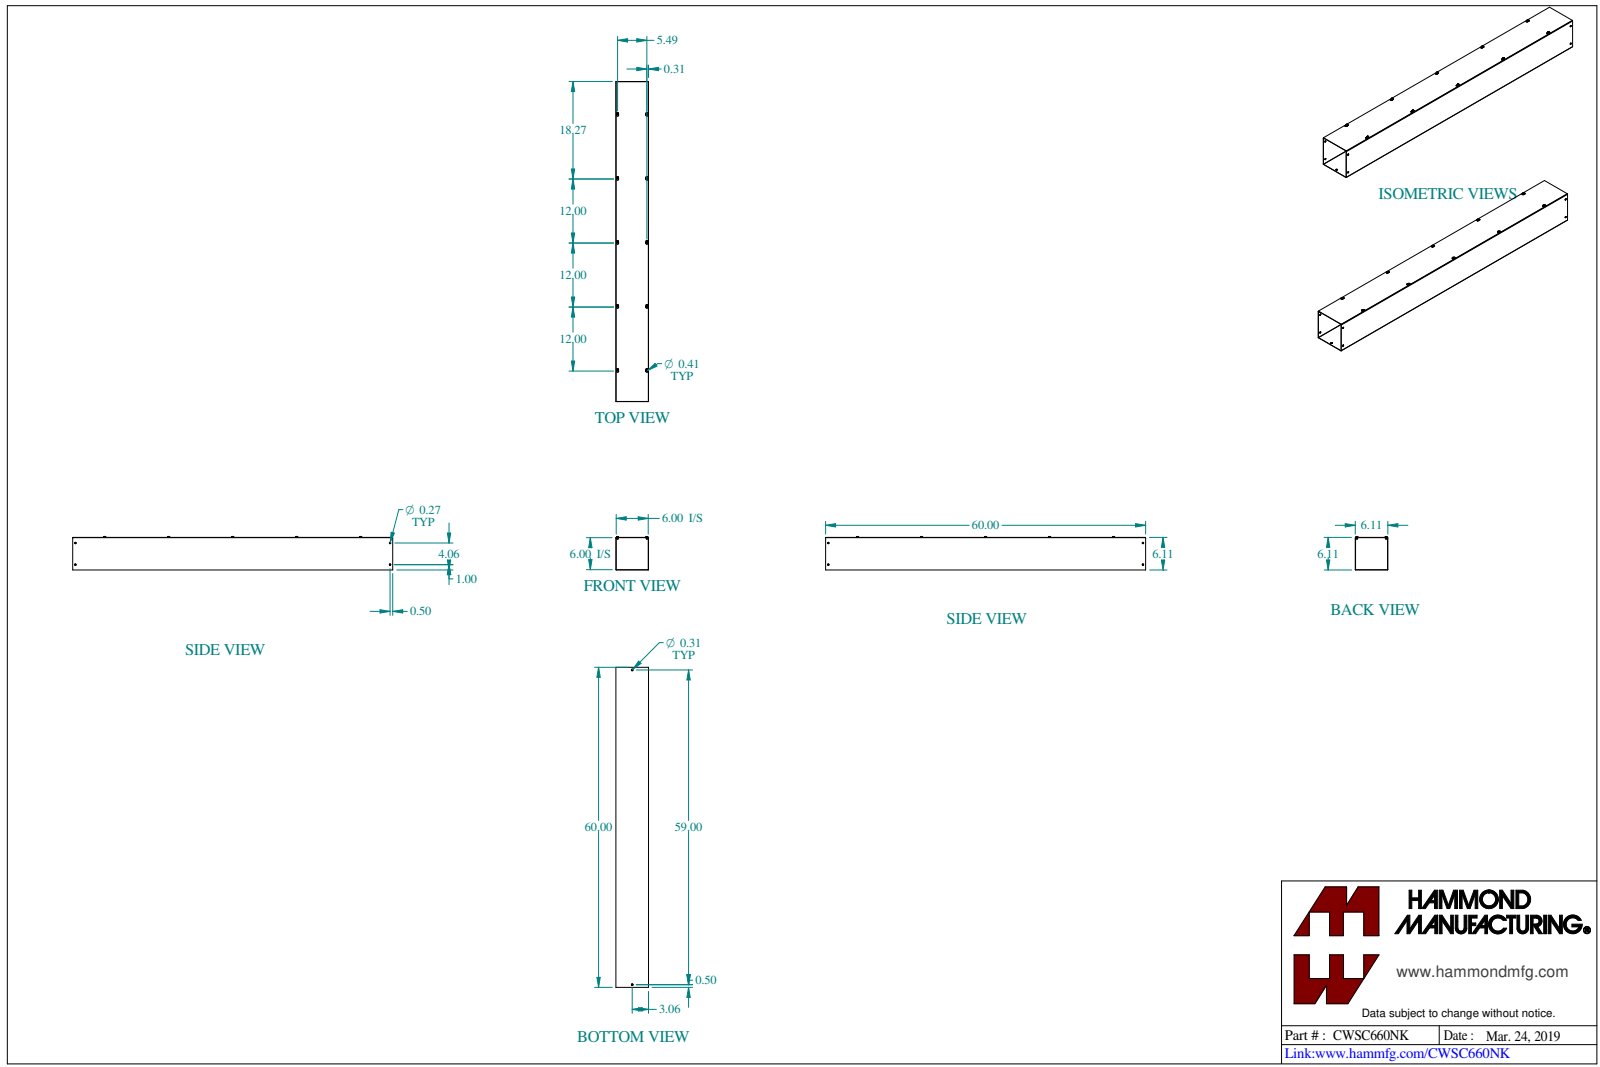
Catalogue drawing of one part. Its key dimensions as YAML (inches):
part_name: "CWSC660NK"
step_written_by: "SolidWorks 2023 (CONFIG_CONTROL_DESIGN)"
units: inches
bodies: {solids: 12, faces: 366, planar: 178, cylindrical: 128, other: 60}
overall_size: [60, 6.289, 6.114]
volume: 85.35
surface_area: 3010
round_holes:
  - {diameter: 0.177, count: 10}
  - {diameter: 0.266, count: 4}
  - {diameter: 0.313, count: 2}
round_bosses_or_shafts:
  - {diameter: 0.375, count: 10}
  - {diameter: 0.19, count: 10}
partial_cylinders:
  - {radius: 0.125, count: 10}
  - {radius: 0.203, count: 10}
  - {radius: 0.029, count: 4}
  - {radius: 0.086, count: 4}
face_to_face_distances: [0.057, 6.057, 6, 6.114, 5.943, 0.114, 0.031, 6.083, 0.026, 6.026]
hole_center_spacings: [12, 13.196, 24, 24.62, 5.489, 6.147, 17.714, 29.628]
